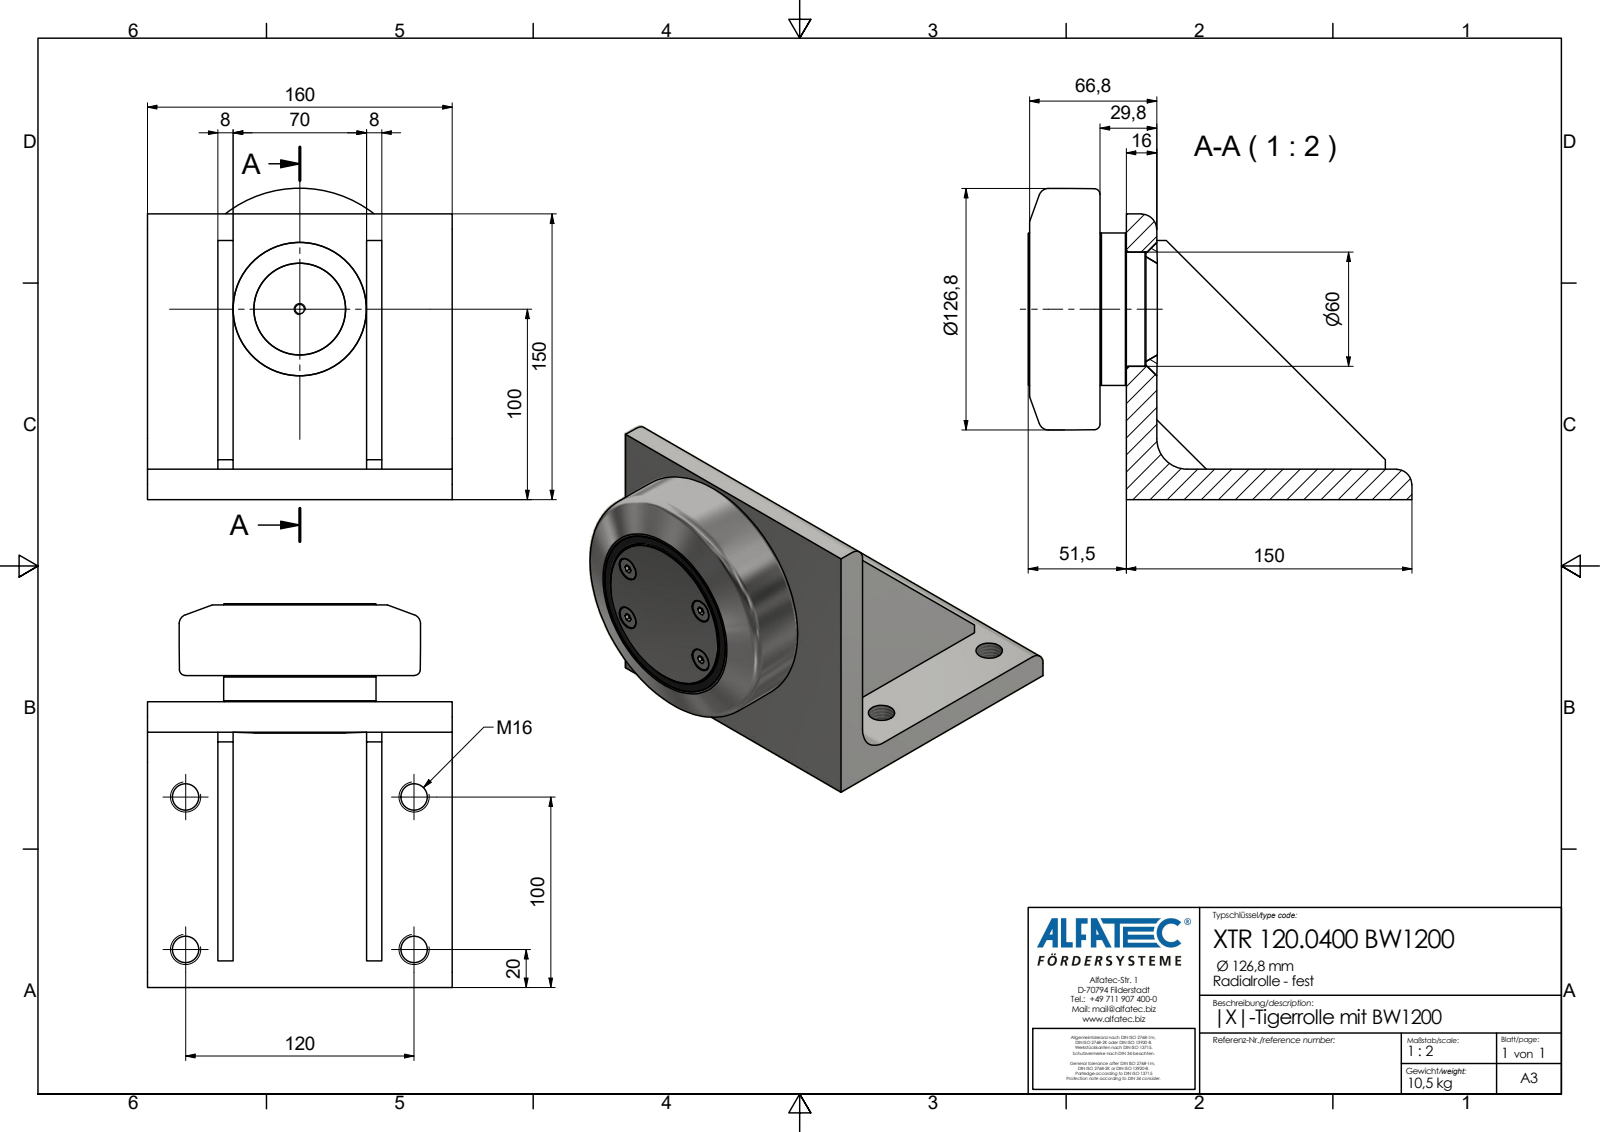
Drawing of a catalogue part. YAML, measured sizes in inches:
part_name: "XTR 120.0400 BW1200_Kontur"
step_written_by: "Autodesk Inventor 2020 (AP242_MANAGED_MODEL_BASED_3D_ENGINEERING_MIM_LF)"
units: inches
bodies: {solids: 1, faces: 89, planar: 62, cylindrical: 19, other: 8}
overall_size: [7.933, 6.433, 6.299]
volume: 82.99
surface_area: 256.8
round_holes:
  - {diameter: 0.488, count: 4}
  - {diameter: 0.545, count: 4}
  - {diameter: 0.194, count: 1}
round_bosses_or_shafts:
  - {diameter: 0.461, count: 4}
  - {diameter: 3.15, count: 1}
partial_cylinders:
  - {radius: 0.315, count: 2}
  - {radius: 0.63, count: 1}
face_to_face_distances: [0.63, 0.315, 3.071, 1.457, 1.772, 4.528, 4.843, 3.386, 2.756, 1.173]
hole_center_spacings: [1.23, 1.23, 2.131, 2.46, 3.15, 4.724, 5.678]
